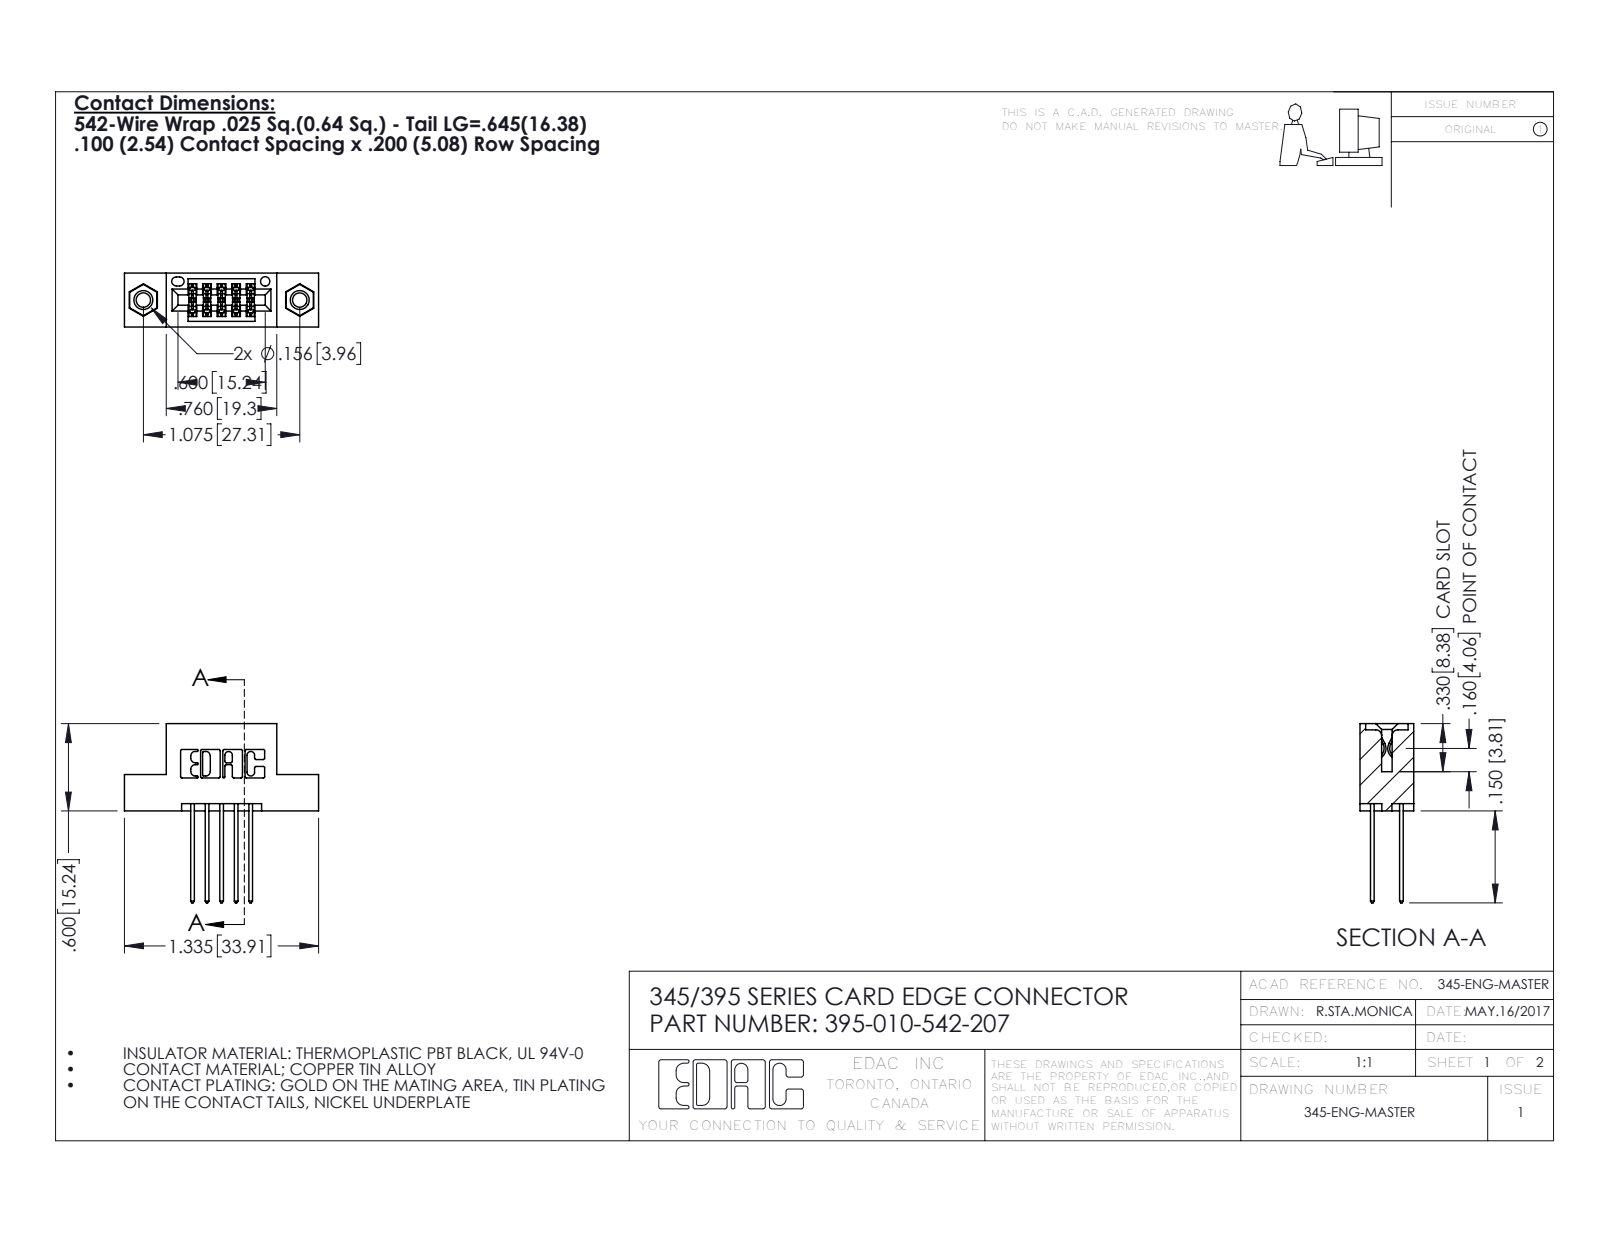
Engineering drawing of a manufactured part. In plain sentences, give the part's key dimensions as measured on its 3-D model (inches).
The part is named "395-010-542-207; 345 Part_Flush Mounting Lugs - 0.156 Dia-TI; 345-292-001_345-293-142; 345-250-001_345-250-005-103". Its 3-D file was written by "SolidWorks 2016 (CONFIG_CONTROL_DESIGN)". It is 13 solids with 686 faces: 442 planar, 228 cylindrical and 16 other. Overall it measures 1.335 by 1.232 by 0.37 inches. Its volume is 0.182 cubic inches and its surface area 6.106 square inches. Round holes: 2 of diameter 0.098, 2 of diameter 0.125, 2 of diameter 0.156, 1 of diameter 0.064. Round bosses or shafts: 2 of diameter 0.155. Partial cylindrical surfaces (rounded edges, fillets, slot ends): 22 of radius 0.01, 15 of radius 0.006, 10 of radius 0.01, 6 of radius 0.007, 6 of radius 0.031, 3 of radius 0.026, 2 of radius 0.014, 2 of radius 0.019. The main face-to-face distances are 0.2, 0.072, 0.298, 0.1, 0.37, 0.098, 0.272, 0.025, 0.225, 0.35. The hole center spacings are 0.27, 0.847, 1.075.
